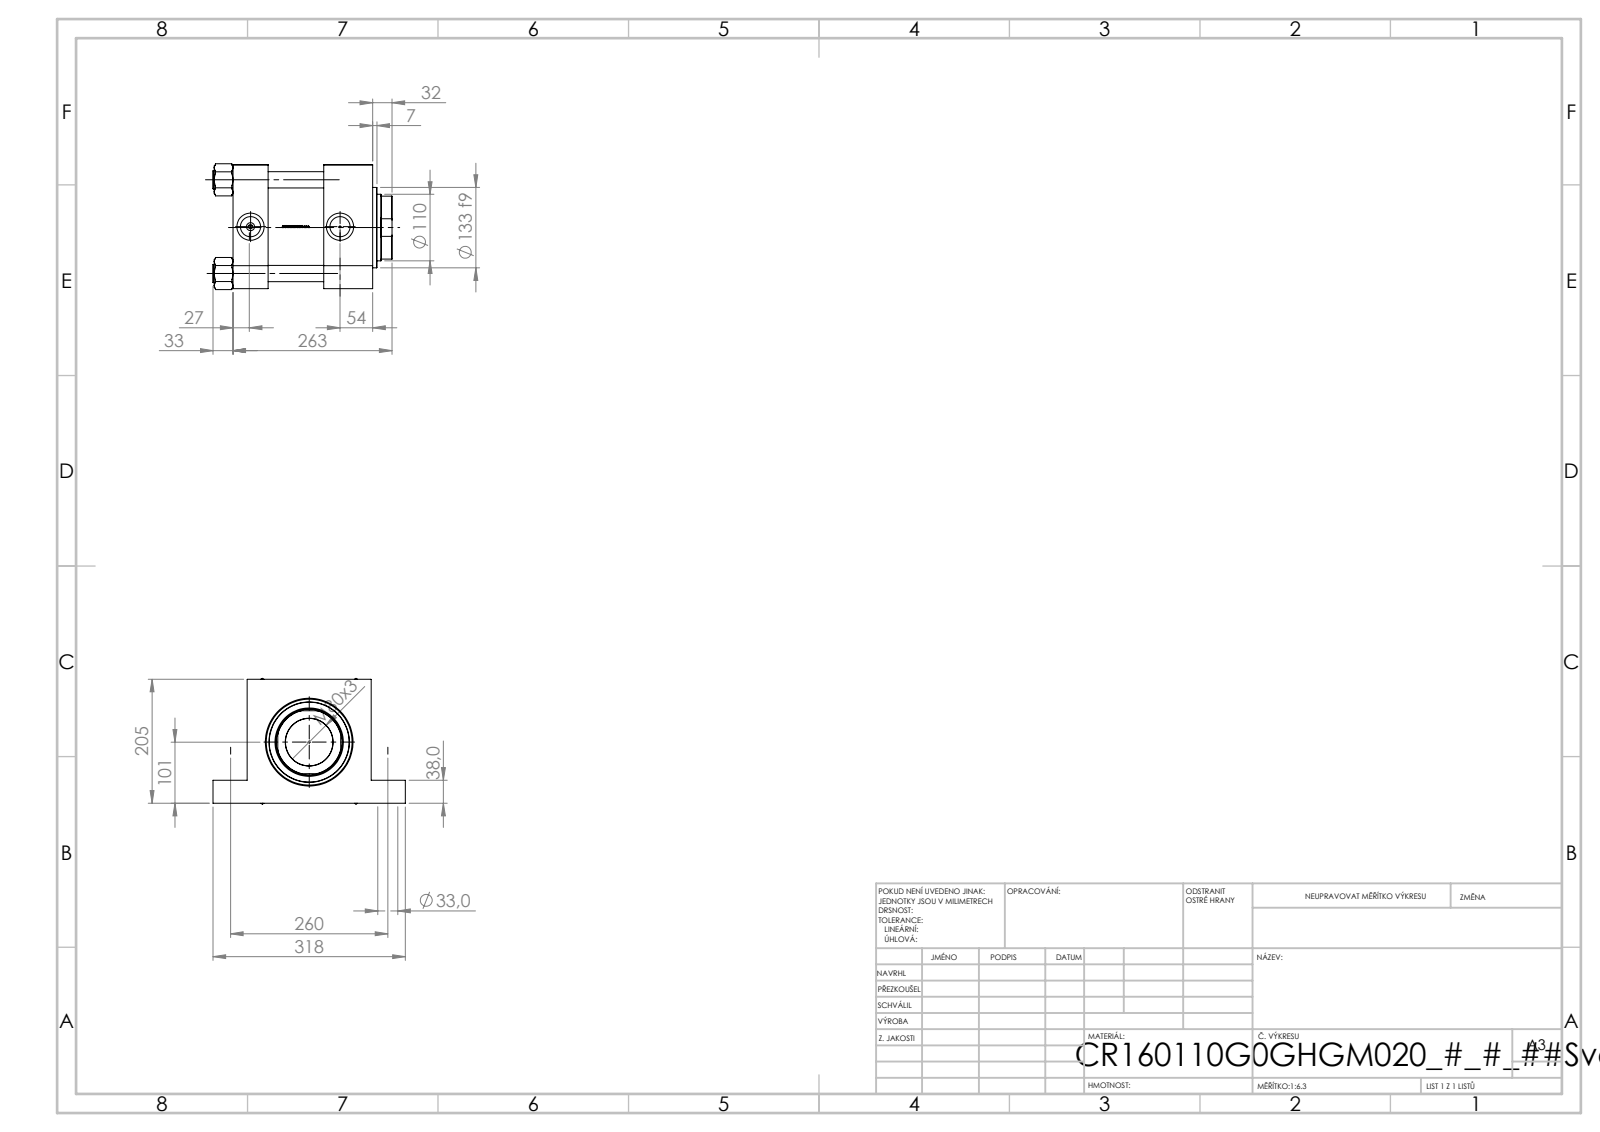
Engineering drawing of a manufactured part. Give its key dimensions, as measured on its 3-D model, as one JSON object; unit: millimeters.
{"part_name": "V215CR_G_Body; V215CR_VCP_G; V215CR_G_TYCINKA; V215_VC_A (+1 more)", "step_written_by": "SolidWorks 2019 (CONFIG_CONTROL_DESIGN)", "units": "millimeters", "bodies": {"solids": 11, "faces": 1135, "planar": 479, "cylindrical": 124, "other": 532}, "overall_size": [318, 296, 208.14], "volume_mm3": 8186000, "surface_area_mm2": 767563, "round_holes": [[27, 4], [33, 4], [7, 2], [33.24, 2], [45, 2], [78.5, 1], [110, 1], [113, 1], [120, 1], [142, 1], [160, 1]], "round_bosses_or_shafts": [[30, 4], [166, 1], [133, 1]], "partial_cylinders_radius": [[54, 1]], "face_to_face_distances": [205, 58, 231, 173, 81, 150, 92, 38, 167, 202.3], "hole_center_spacings": [154.9, 108.48, 110.6, 150, 219.06, 260, 300.17, 148]}
